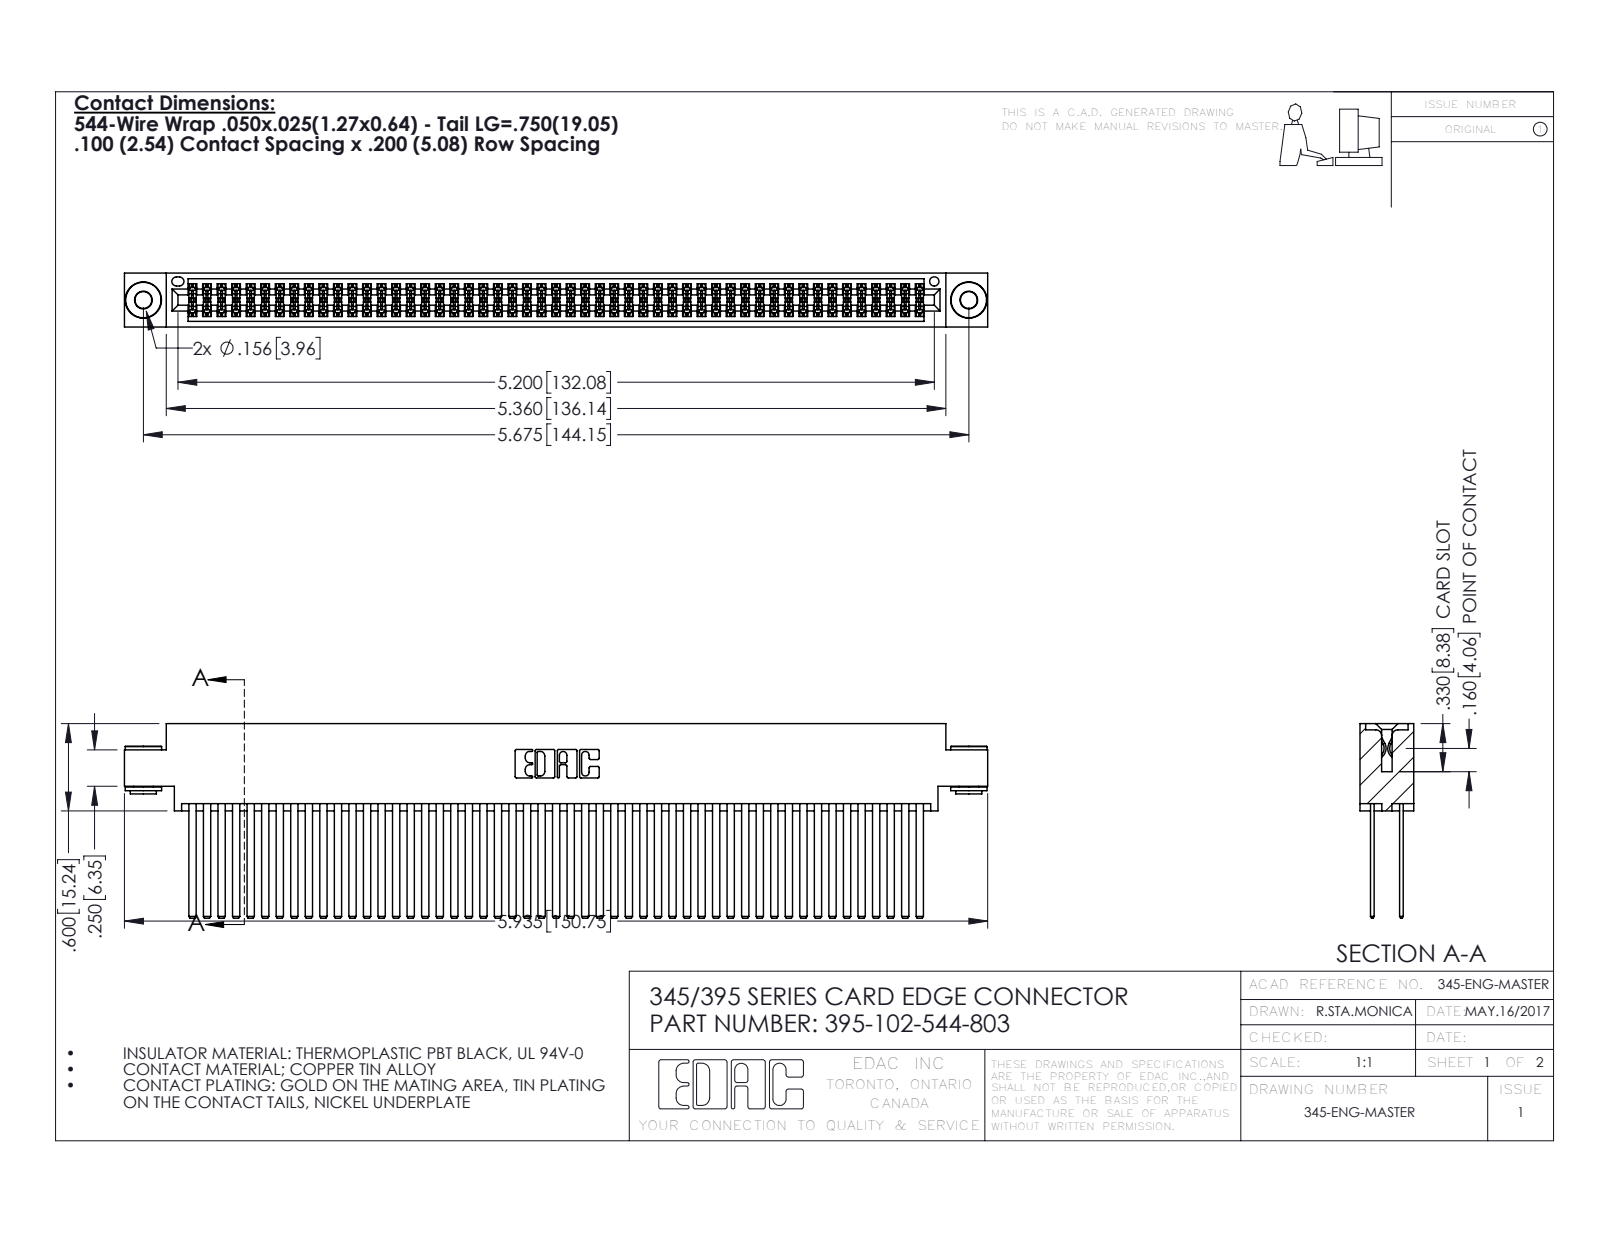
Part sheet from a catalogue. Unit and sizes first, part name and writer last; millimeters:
Units: millimetres
Overall size (bounding box): 150.7 × 34 × 9.4
Round holes (diameter × count): ⌀2.9 ×2, ⌀4 ×2, ⌀1.6 ×1
Round bosses / shafts (diameter × count): ⌀6.4 ×2, ⌀4.6 ×2, ⌀3.5 ×2
Partial cylindrical surfaces — rounded edges, fillets, slot ends (radius × count): R0.2 ×153, R0.3 ×22, R0.2 ×6, R0.8 ×6, R0.7 ×3, R0.4 ×2, R0.5 ×2, R0.6 ×2
Main face-to-face distances: 5.1, 0.6, 1.8, 2.5, 6.9, 7.6, 5.7, 4.4, 9.4, 3.8
Hole centre spacings: 6.9, 138.2, 144.1
Volume: 16 100 mm³ · Surface area: 28 460 mm²
Bodies: 105 solids, 4656 faces (3052 planar, 1596 cylindrical, 8 other)
Part name (STEP PRODUCT): 395-102-544-803; 345-292-001_345-293-144; 345-250-002_345-250-002-102; 345 Part_0.170 Offset - 0.156 Dia-TH
STEP written by: SolidWorks 2016 (CONFIG_CONTROL_DESIGN)
